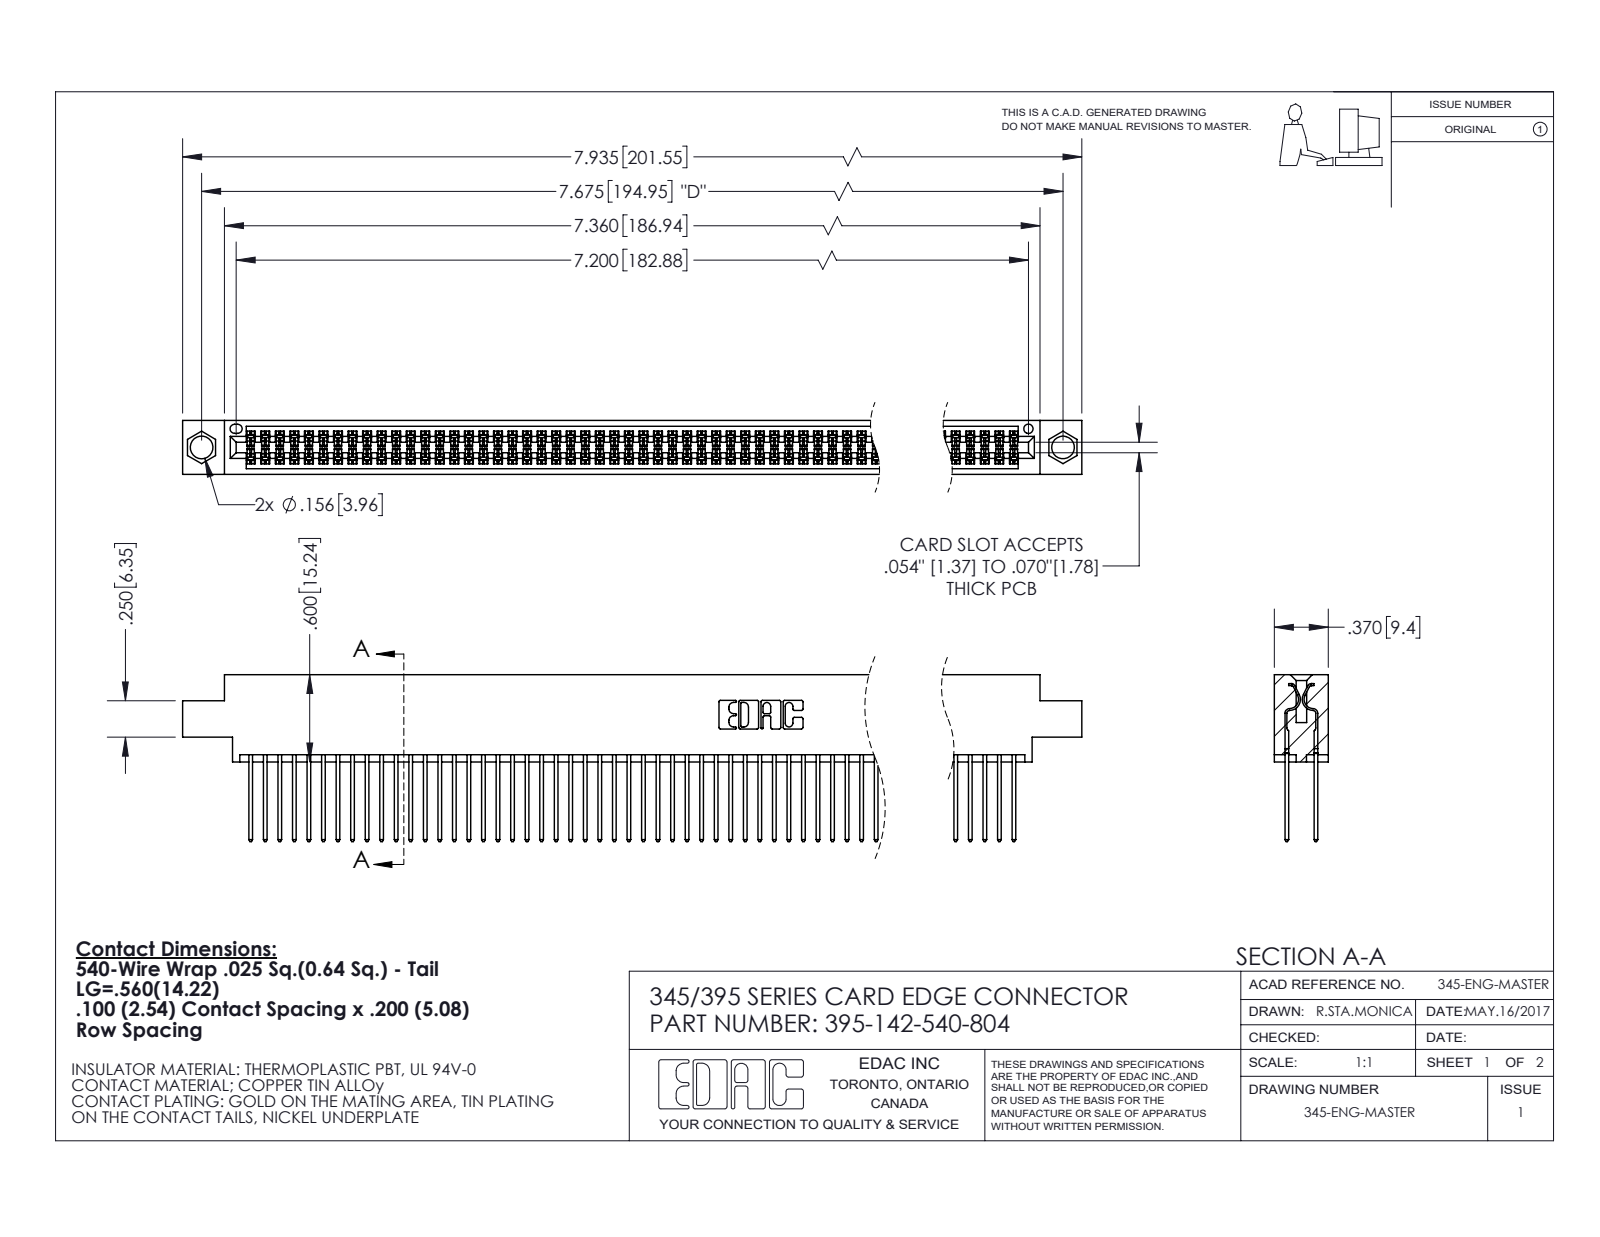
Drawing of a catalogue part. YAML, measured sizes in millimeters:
part_name: "345 Part_0.170 Offset - 0.156 Dia-TI; 395-142-540-804; 345-292-001_345-293-140"
step_written_by: "SolidWorks 2020 (CONFIG_CONTROL_DESIGN)"
units: millimeters
bodies: {solids: 143, faces: 7244, planar: 4784, cylindrical: 2460, other: 0}
overall_size: [201.5, 29.1, 9.4]
volume: 20170
surface_area: 32860
round_holes:
  - {diameter: 4, count: 2}
  - {diameter: 1.6, count: 1}
partial_cylinders:
  - {radius: 0.2, count: 213}
  - {radius: 0.3, count: 142}
  - {radius: 0.3, count: 22}
  - {radius: 0.2, count: 6}
  - {radius: 0.8, count: 6}
  - {radius: 0.7, count: 3}
  - {radius: 0.4, count: 2}
  - {radius: 0.5, count: 2}
face_to_face_distances: [7.6, 1.8, 5.1, 2.5, 6.9, 0.6, 9.4, 5.7, 4.4, 3.8]
hole_center_spacings: [6.9, 189, 194.9]
